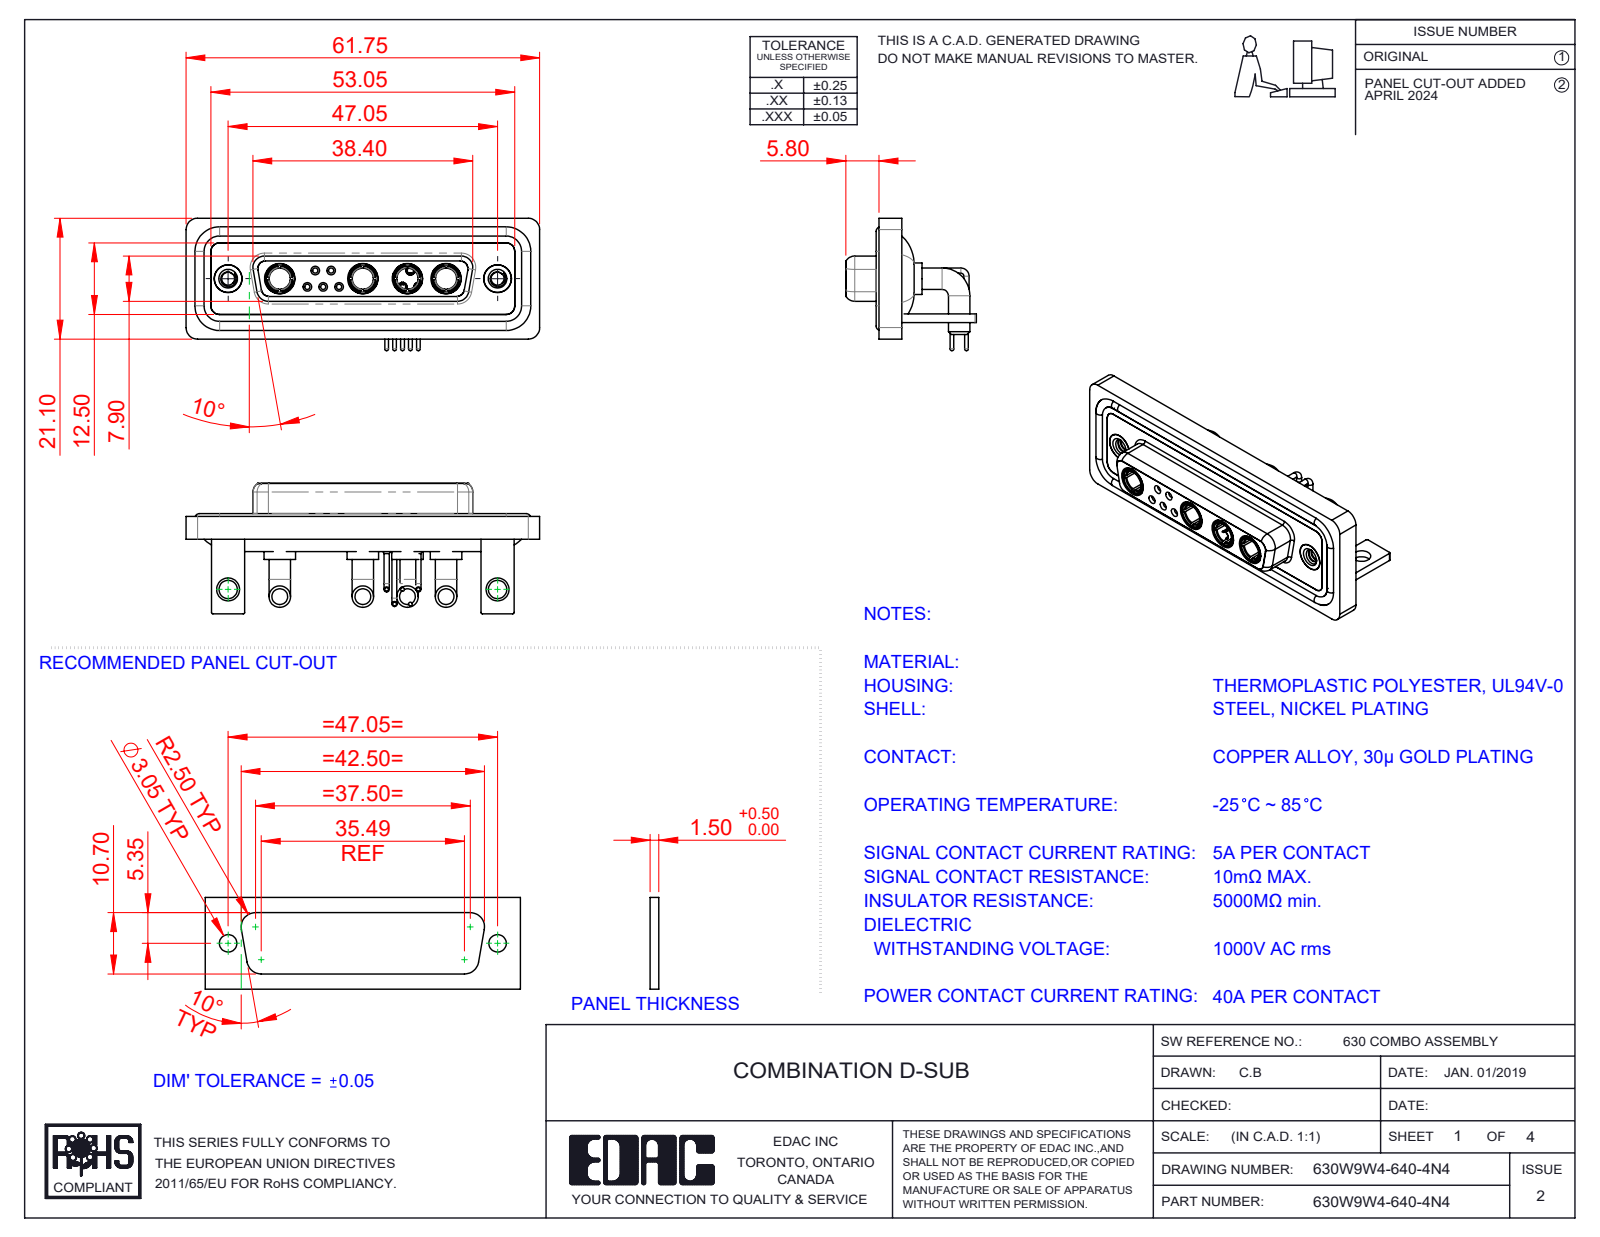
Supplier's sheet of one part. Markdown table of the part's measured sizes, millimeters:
| quantity | value |
| --- | --- |
| part name | 630Combo Waterproof Housing_25 Contacts; 630Combo Contact Row 2_50 Contacts; 630Combo Shell Rear_25 Contacts; 630Combo Stabilizer Bracket_50 Contacts (+6 more) |
| STEP written by | SolidWorks 2023 (CONFIG_CONTROL_DESIGN) |
| units | millimeters |
| bodies | 22 solids, 1011 faces (316 planar, 427 cylindrical, 268 other) |
| overall size | 61.75 × 23.12 × 22.8 |
| volume | 9 109 mm³ |
| surface area | 14 957 mm² |
| round holes (diameter × count) | 4.85 × 6, 0.9 × 5, 1.1 × 5, 1.5 × 5, 2 × 5, 3.7 × 4, 5.3 × 4, 1.6 × 3, 1.7 × 2, 2.26 × 2, 3.2 × 2, 4 × 2 |
| round bosses / shafts (diameter × count) | 0.9 × 10, 1.6 × 9, 3.75 × 8, 2 × 5, 1.5 × 5, 0.65 × 5, 5.5 × 4, 5.2 × 4 |
| partial cylindrical surfaces (radius × count) | 2 × 19, 1.5 × 18, 0.25 × 16, 1.35 × 8, 1.6 × 8, 0.5 × 5, 0.6 × 4, 0.65 × 4 |
| main face-to-face distances | 0.4, 1.8, 2.9, 3.7, 1.5, 4.1, 1.1, 1.4, 1.6, 2.5 |
| hole center spacings | 3.16, 2.77, 5.04, 13.85, 11.08, 12.79, 15.5, 5.54 |
